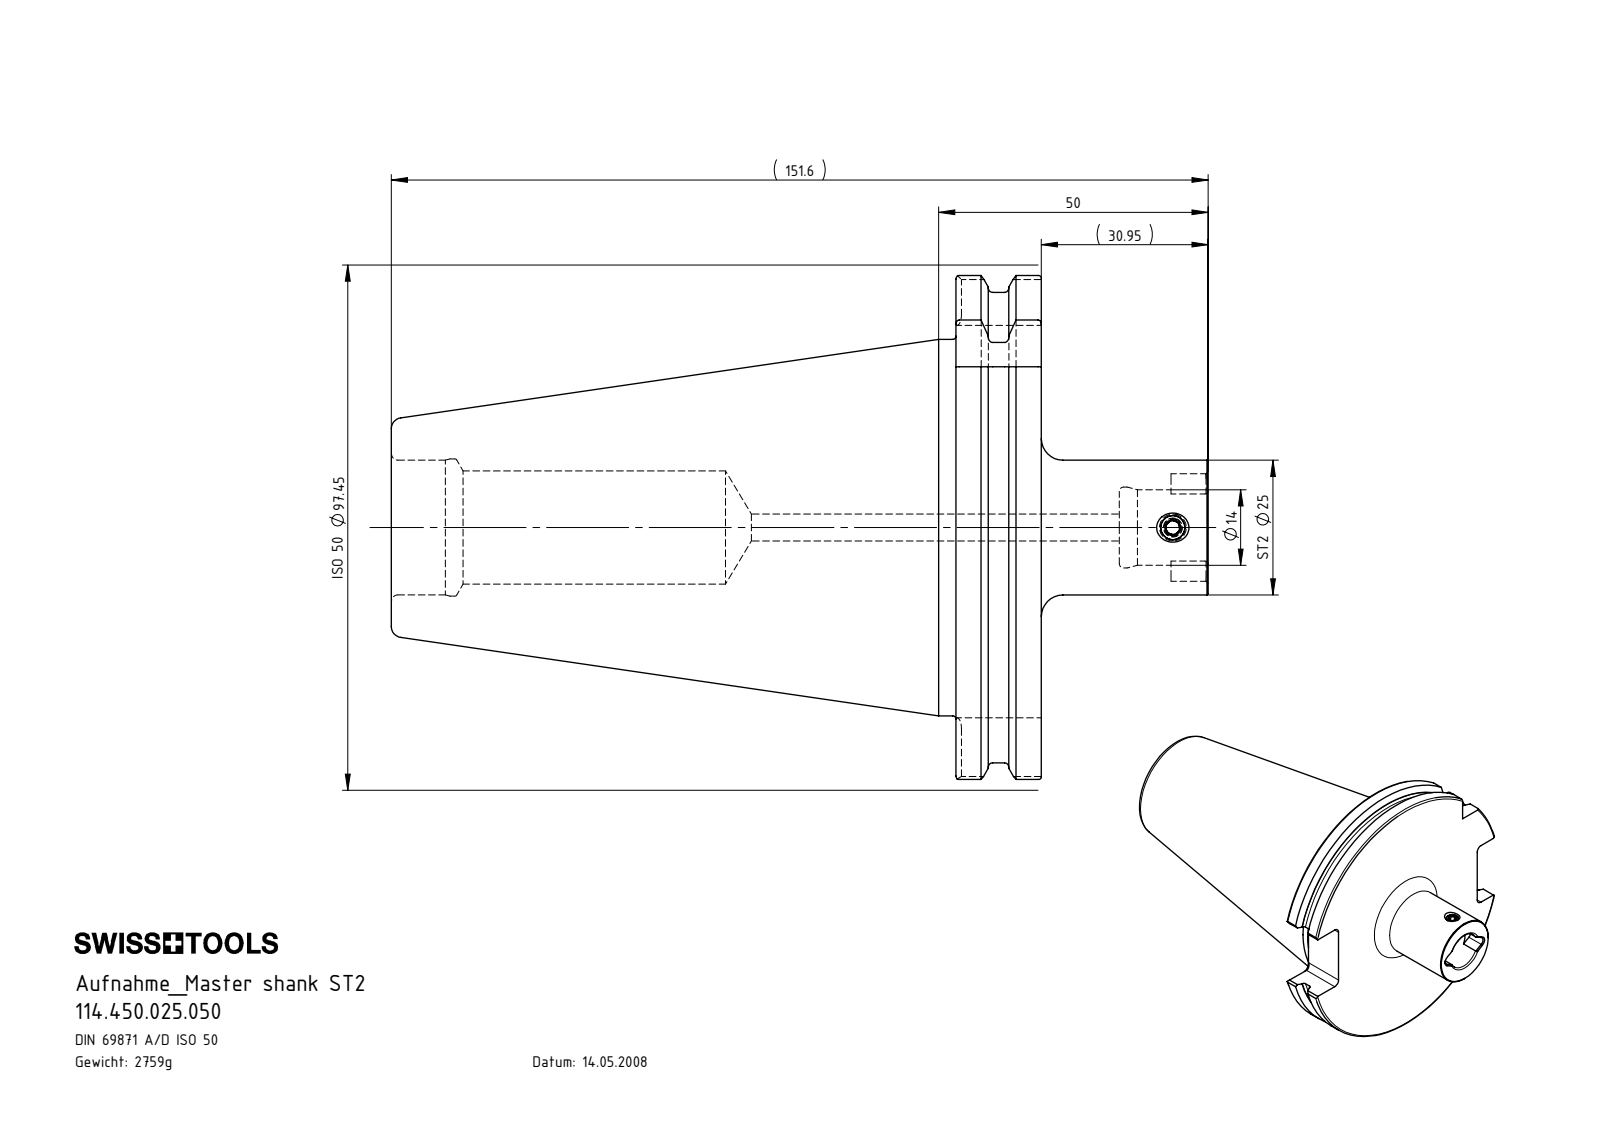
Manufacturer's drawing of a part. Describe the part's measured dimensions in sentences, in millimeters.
The part is named "SK5-ST2.K01.050; SK5-ST2.K01.050_A". Its 3-D file was written by "SolidWorks 2015 (CONFIG_CONTROL_DESIGN)". It is 1 solid with 131 faces: 40 planar, 38 cylindrical and 53 other. Overall it measures 151.6 by 97.45 by 93.51 millimeters. Its volume is 351 356 cubic millimeters and its surface area 43 845 square millimeters. Round holes: 1 of diameter 4.5, 1 of diameter 5, 1 of diameter 14, 1 of diameter 15, 1 of diameter 21, 1 of diameter 25, 1 of diameter 25.45. Round bosses or shafts: 1 of diameter 91, 1 of diameter 69.85. Partial cylindrical surfaces (rounded edges, fillets, slot ends): 8 of radius 2, 2 of radius 1.8, 1 of radius 48.73. The main face-to-face distances are 15.85, 104.8, 120.65, 72.8, 151.6, 46.8, 30.95, 25.7, 135.1, 30.3.
